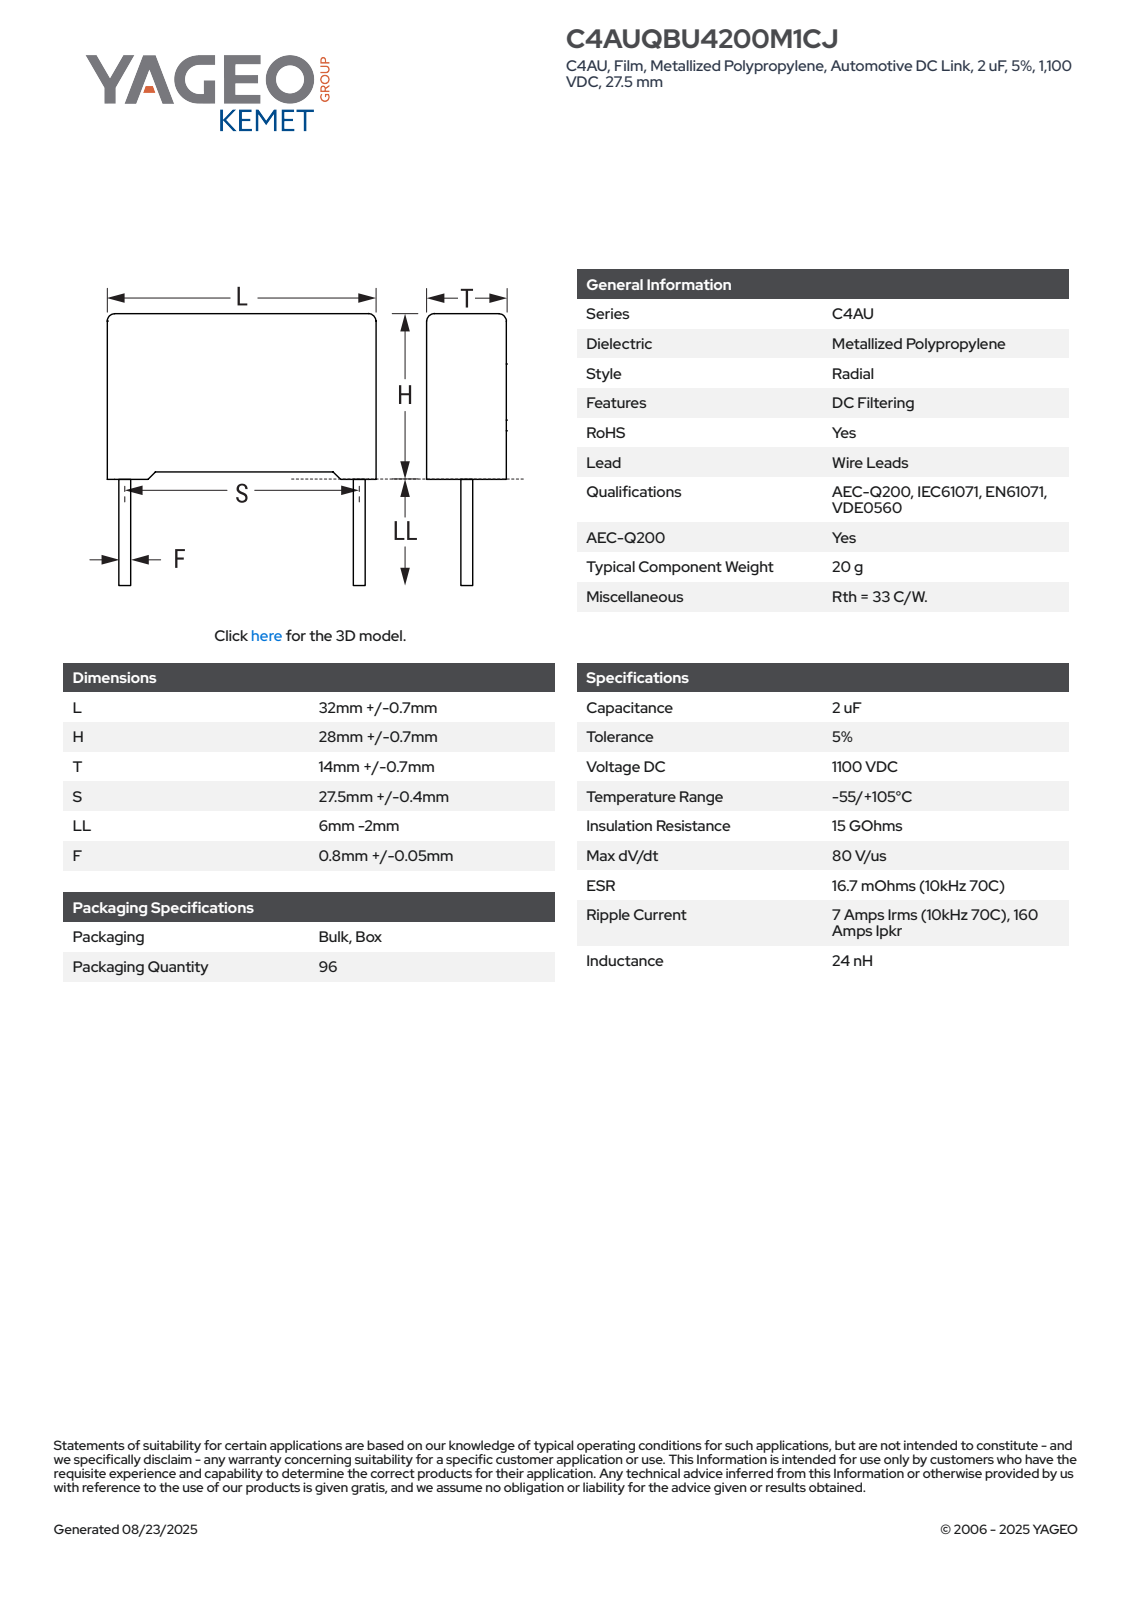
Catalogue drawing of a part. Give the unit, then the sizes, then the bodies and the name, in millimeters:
Units: millimetres
Overall size (bounding box): 32.7 × 32.7 × 14.71
Round bosses / shafts (diameter × count): ⌀0.85 ×2
Partial cylindrical surfaces — rounded edges, fillets, slot ends (radius × count): R0.5 ×4
Main face-to-face distances: 14.7, 32.7, 27.71, 27.95, 0.75, 0.99, 28.7, 1.09, 14.71, 31.61
Volume: 13 390 mm³ · Surface area: 3 754 mm²
Bodies: 4 solids, 85 faces (77 planar, 8 cylindrical, 0 other)
Part name (STEP PRODUCT): CFR_RB2CFP_32X28X14_L32.7H28.7T14.7S27.5LL4F0.85
STEP written by: SolidWorks 2014 (AUTOMOTIVE_DESIGN)
